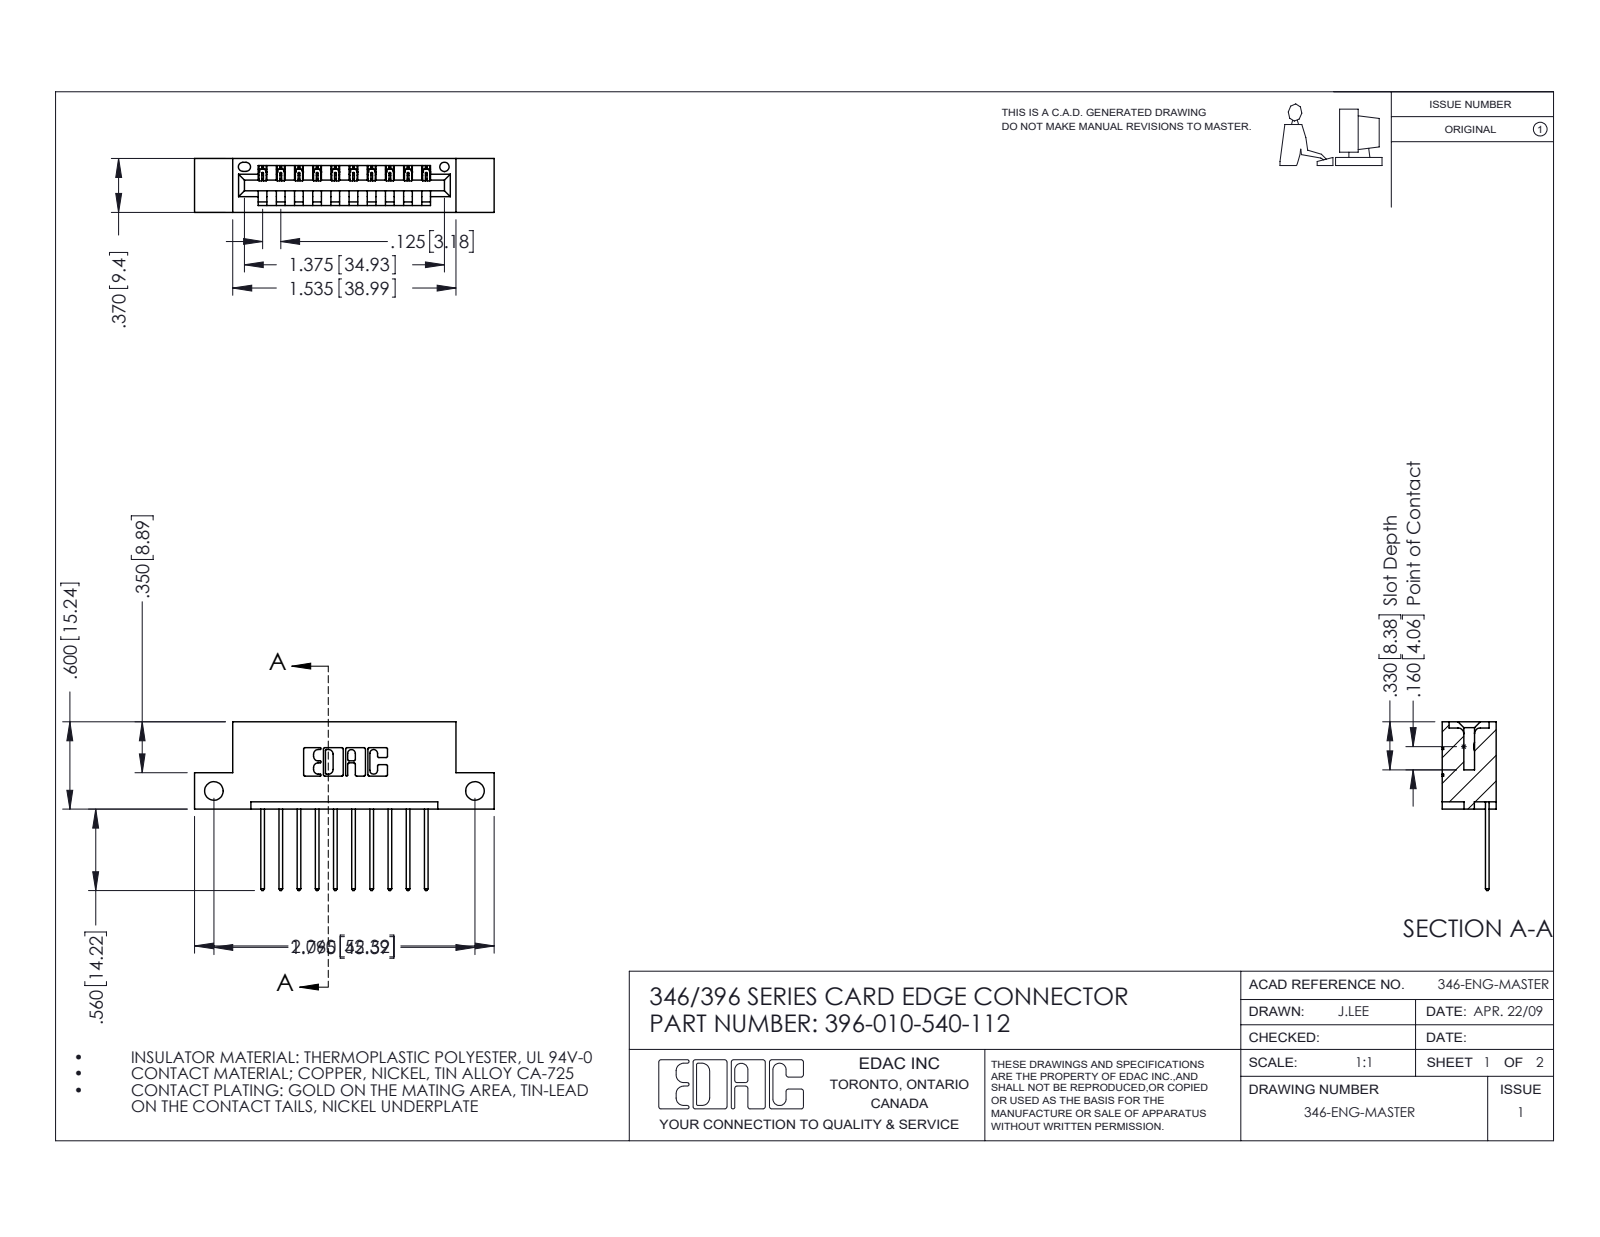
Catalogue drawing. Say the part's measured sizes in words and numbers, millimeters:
The part is named "346 Part_Flush Mounting Lugs - Side Mount; 345-292-001_345-293-140; 396-010-540-112". Its 3-D file was written by "SolidWorks 2016 (CONFIG_CONTROL_DESIGN)". It is 11 solids with 702 faces: 476 planar, 226 cylindrical and 0 other. Overall it measures 52.3 by 29.5 by 9.4 millimeters. Its volume is 4 720 cubic millimeters and its surface area 5 500 square millimeters. Round holes: 2 of diameter 3.3, 1 of diameter 1.6. Partial cylindrical surfaces (rounded edges, fillets, slot ends): 22 of radius 0.3, 20 of radius 0.2, 20 of radius 0.3, 6 of radius 0.2, 6 of radius 0.8, 3 of radius 0.7, 2 of radius 0.8, 2 of radius 1. The main face-to-face distances are 6.4, 1.2, 8.2, 9.4, 1.8, 7.6, 0.6, 3.8, 5.6, 2.5. The hole center spacings are 45.6.
